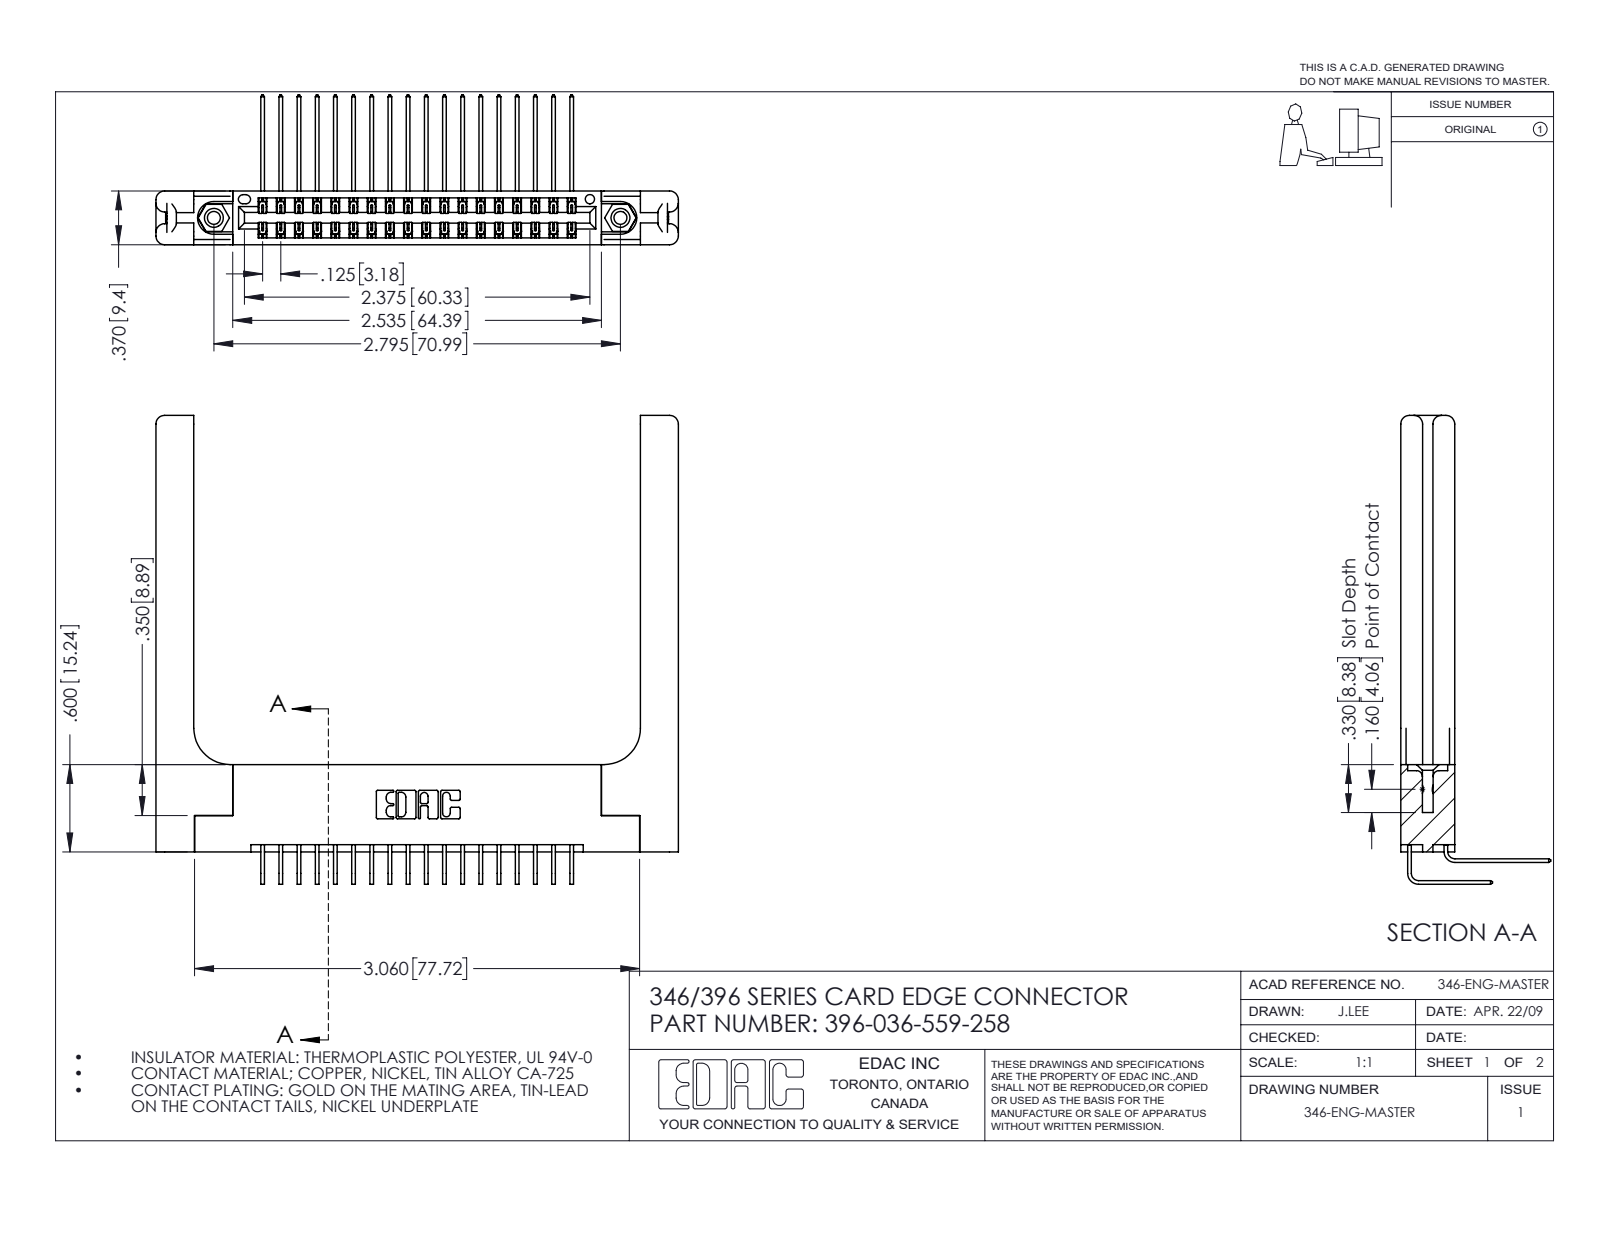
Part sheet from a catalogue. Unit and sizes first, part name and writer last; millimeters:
Units: millimetres
Overall size (bounding box): 91.2 × 81.9 × 26.2
Round holes (diameter × count): ⌀2.3 ×2, ⌀3.2 ×2, ⌀4 ×2, ⌀1.6 ×1
Round bosses / shafts (diameter × count): ⌀3.9 ×2
Partial cylindrical surfaces — rounded edges, fillets, slot ends (radius × count): R0.2 ×54, R0.3 ×22, R1.5 ×16, R0.2 ×6, R0.8 ×6, R0.7 ×3, R0.4 ×2, R0.6 ×2
Main face-to-face distances: 9.4, 1.8, 8.2, 1.2, 3.8, 3.8, 0.6, 6.4, 7.6, 2
Hole centre spacings: 6.2, 65.7, 71
Volume: 16 400 mm³ · Surface area: 17 850 mm²
Bodies: 41 solids, 2322 faces (1556 planar, 706 cylindrical, 60 other)
Part name (STEP PRODUCT): 345-292-001_558 559 Tail - 1; 345-292-001_559 Tail - 2; 396-036-559-258; 346 Part_Flush Mounting Lugs - 0.156 Dia-TH (+2 more)
STEP written by: SolidWorks 2016 (CONFIG_CONTROL_DESIGN)
